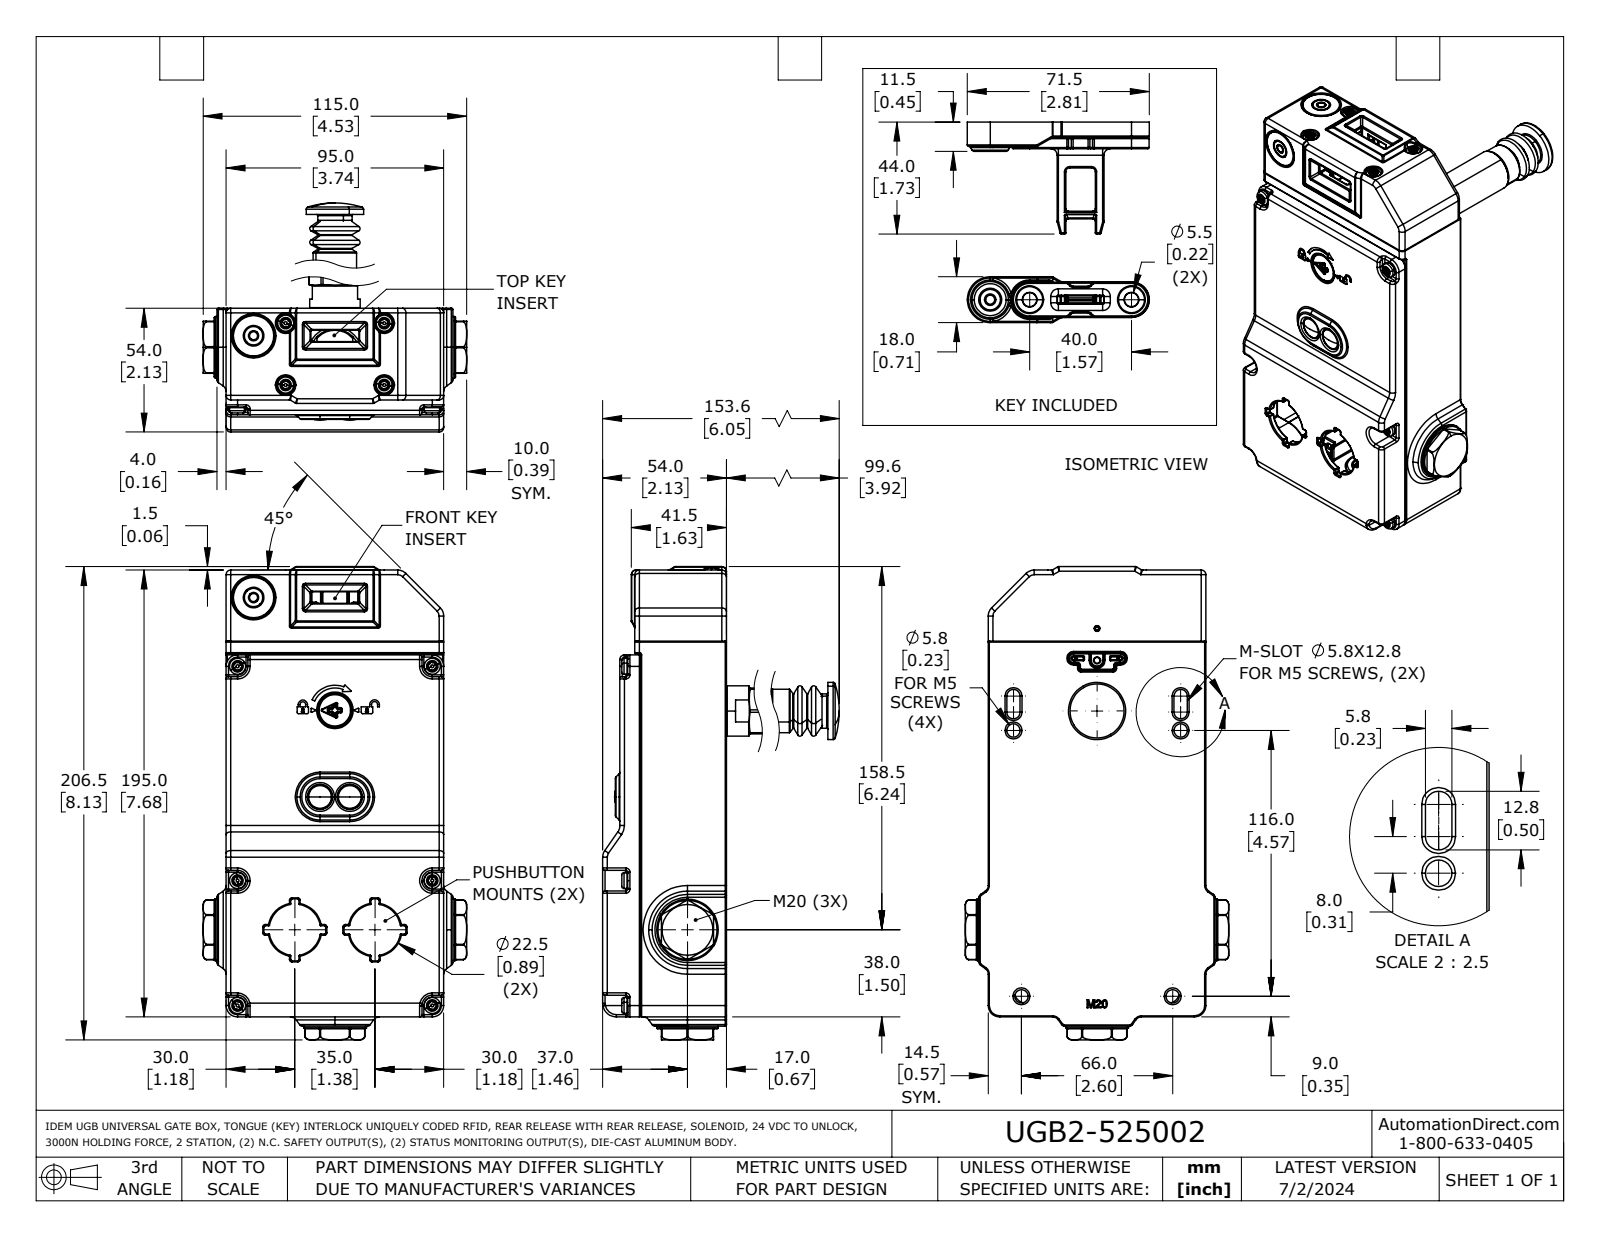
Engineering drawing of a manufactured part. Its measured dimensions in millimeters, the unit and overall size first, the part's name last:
Units: millimetres
Overall size (bounding box): 219 × 153.6 × 115
Round holes (diameter × count): ⌀3.3 ×10, ⌀4 ×10, ⌀2.5 ×8, ⌀4.5 ×8, ⌀8 ×8, ⌀5 ×5, ⌀12 ×5, ⌀4.2 ×4, ⌀5.5 ×4, ⌀5.8 ×4, ⌀9 ×4, ⌀14 ×3
Round bosses / shafts (diameter × count): ⌀3.5 ×12, ⌀7 ×10, ⌀1.3 ×10, ⌀6.2 ×6, ⌀6 ×4, ⌀18 ×3, ⌀16 ×3, ⌀26.8 ×2
Partial cylindrical surfaces — rounded edges, fillets, slot ends (radius × count): R0.5 ×622, R1 ×205, R0.2 ×131, R0.3 ×106, R2 ×36, R0.4 ×22, R0.7 ×20, R0.8 ×16
Main face-to-face distances: 3, 2.2, 92, 7.5, 95, 46.5, 44.3, 43.5, 51, 4.5
Hole centre spacings: 25.39, 75.61, 126.36, 15.5, 36.39, 41.86, 85, 2.83
Volume: 312 118 mm³ · Surface area: 193 807 mm²
Bodies: 29 solids, 5248 faces (1157 planar, 2134 cylindrical, 1957 other)
Part name (STEP PRODUCT): 525002 UGB2-KLTM-RFID-RR (with Manual Override)
STEP written by: SolidWorks 2021 (CONFIG_CONTROL_DESIGN)
